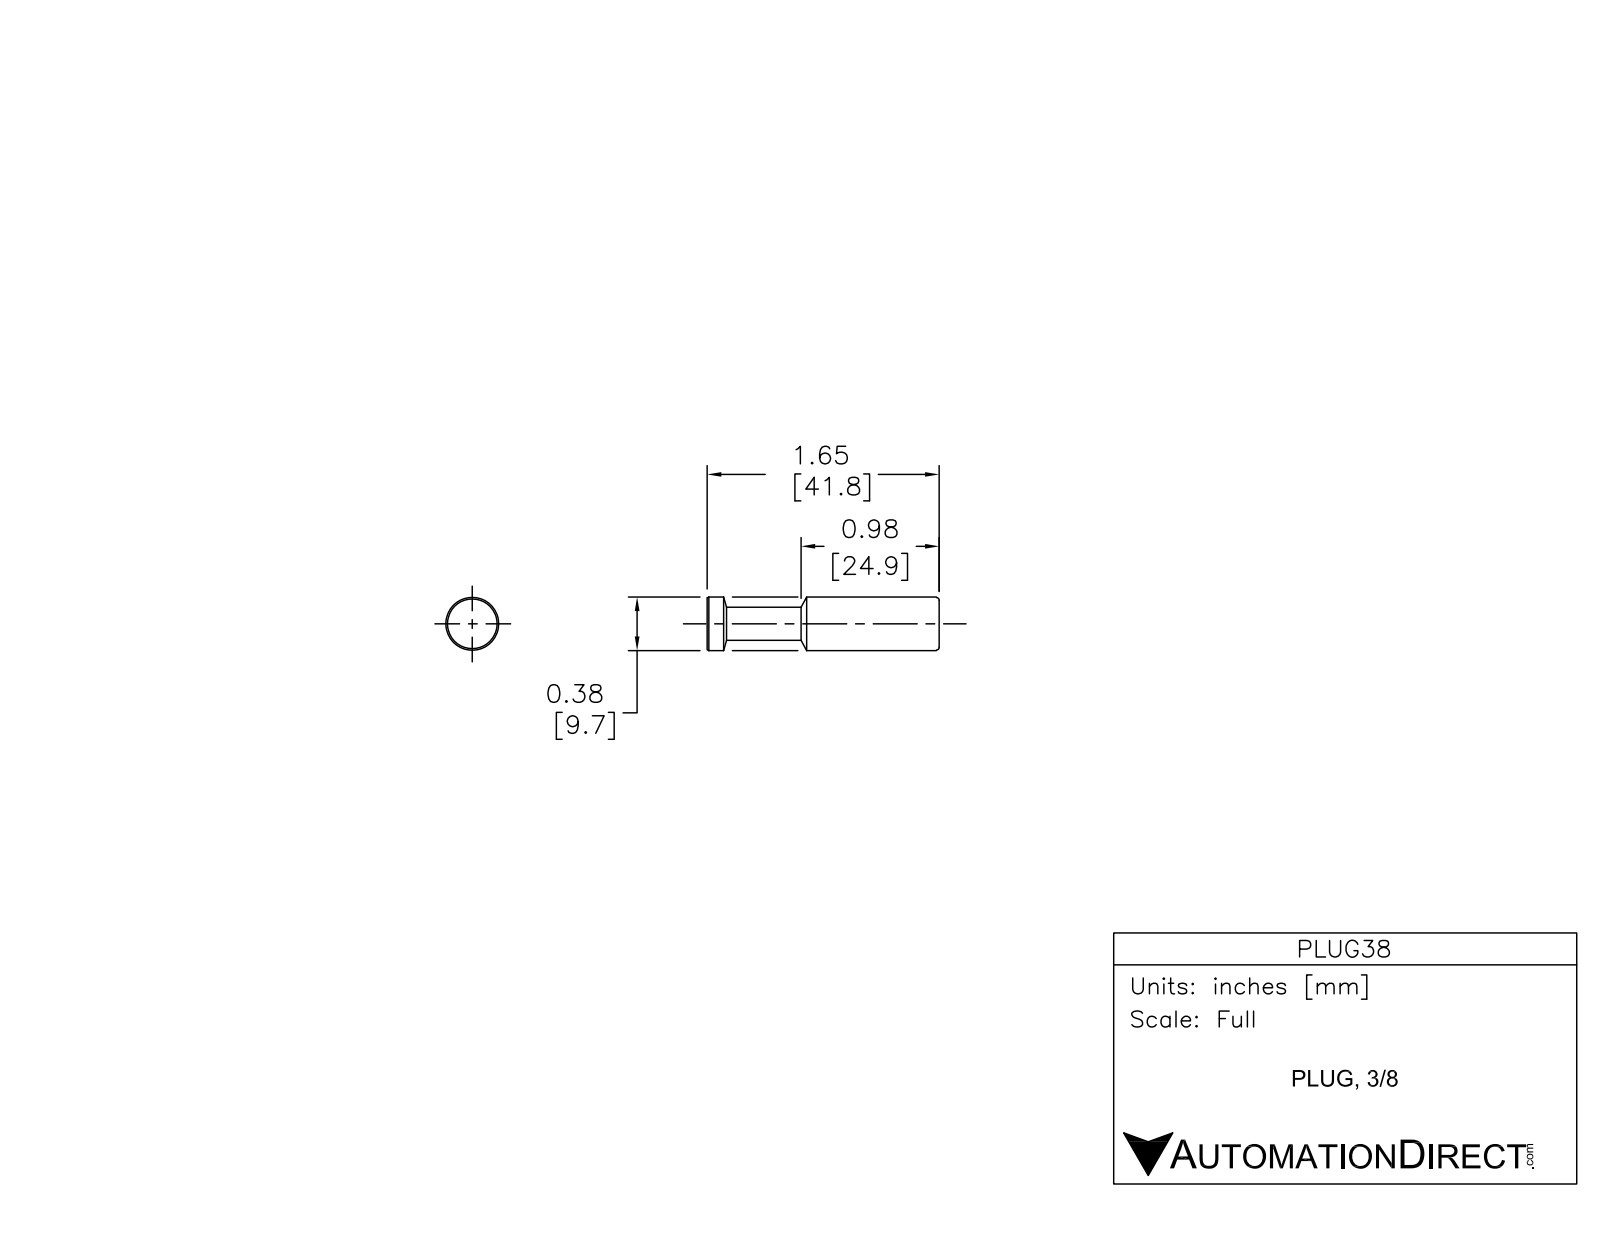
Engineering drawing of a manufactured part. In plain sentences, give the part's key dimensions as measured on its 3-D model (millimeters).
The part is named "PLUG38". Its 3-D file was written by "SolidWorks 2015 (AUTOMOTIVE_DESIGN)". It is 1 solid with 16 faces: 2 planar, 6 cylindrical and 8 other. Overall it measures 42 by 10 by 10 millimeters. Its volume is 2 390 cubic millimeters and its surface area 1 302 square millimeters. Round bosses or shafts: 1 of diameter 10, 1 of diameter 9.5, 1 of diameter 6. The main face-to-face distances are 42.
